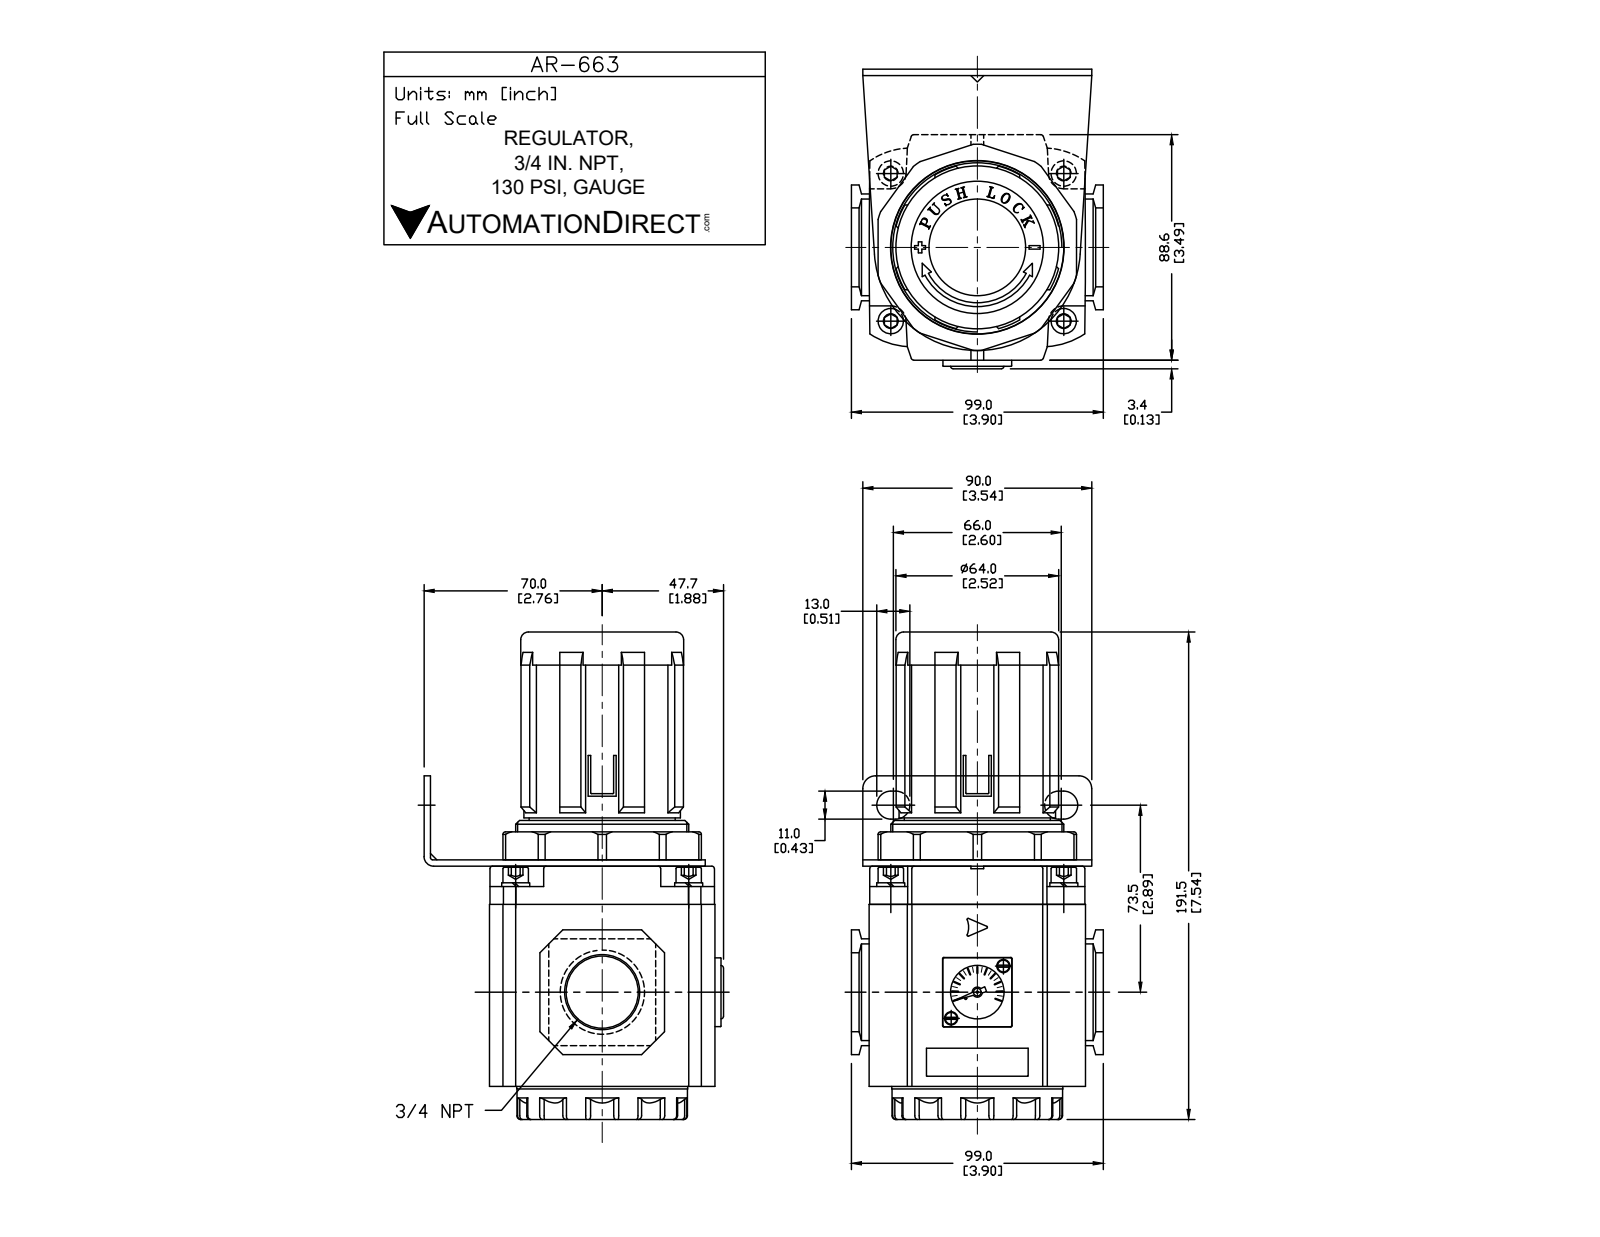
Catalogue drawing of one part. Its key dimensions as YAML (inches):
part_name: "AR-663"
step_written_by: "SolidWorks 2015 (CONFIG_CONTROL_DESIGN)"
units: inches
bodies: {solids: 11, faces: 475, planar: 326, cylindrical: 111, other: 38}
overall_size: [7.539, 4.606, 3.898]
volume: 62.31
surface_area: 186.8
round_holes:
  - {diameter: 0.118, count: 4}
  - {diameter: 0.079, count: 1}
  - {diameter: 0.709, count: 1}
  - {diameter: 0.906, count: 1}
  - {diameter: 1.181, count: 1}
round_bosses_or_shafts:
  - {diameter: 0.394, count: 4}
  - {diameter: 2.677, count: 1}
  - {diameter: 2.638, count: 1}
  - {diameter: 2.585, count: 1}
  - {diameter: 2.52, count: 1}
  - {diameter: 2.117, count: 1}
  - {diameter: 0.157, count: 1}
  - {diameter: 0.031, count: 1}
partial_cylinders:
  - {radius: 0.047, count: 10}
  - {radius: 0.012, count: 4}
  - {radius: 0.039, count: 4}
  - {radius: 0.217, count: 4}
  - {radius: 0.276, count: 4}
  - {radius: 0.783, count: 4}
  - {radius: 0.008, count: 3}
  - {radius: 0.128, count: 2}
face_to_face_distances: [0.098, 3.504, 3.406, 3.622, 3.488, 3.917, 0.276, 3.346, 0.512, 4.016]
hole_center_spacings: [1.628, 2.093, 2.494, 3.256]
